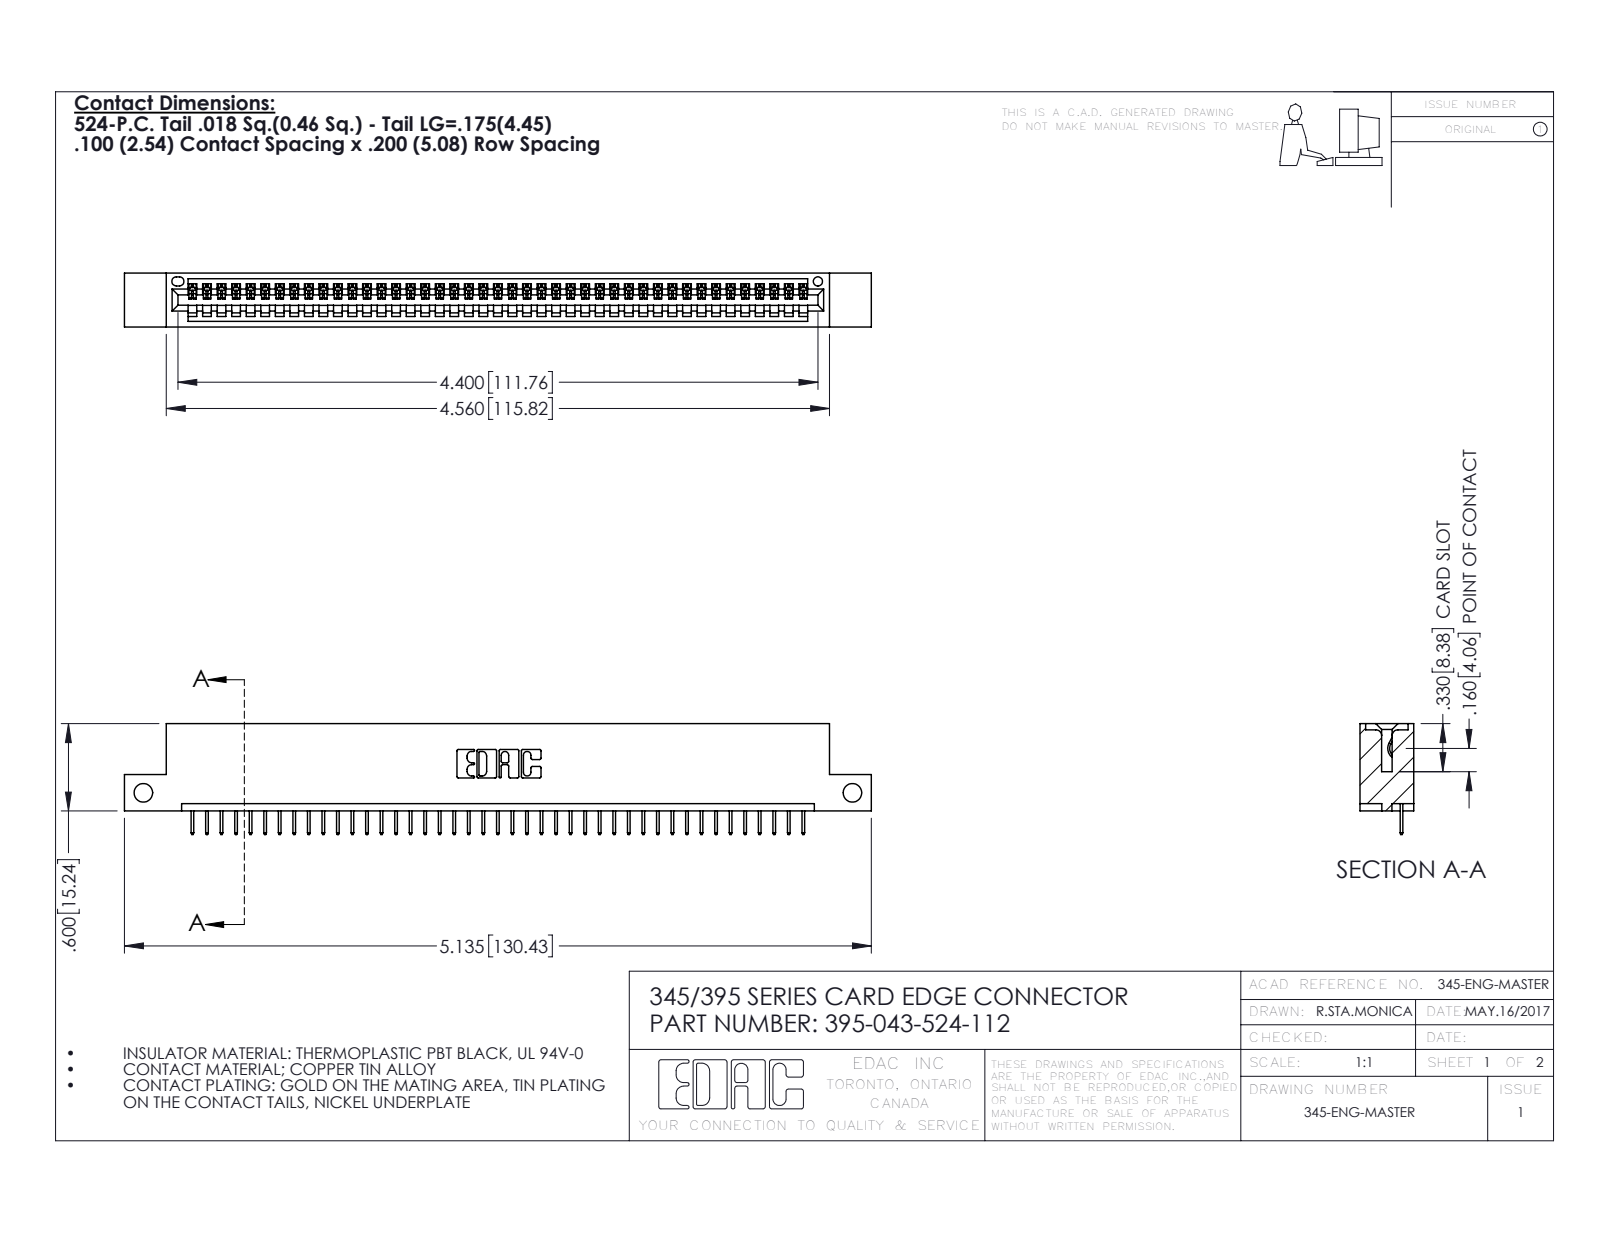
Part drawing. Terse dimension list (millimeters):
name: 395-043-524-112; 345-292-001_345-293-124; 345 Part_Flush Mounting Lugs - Side Mount
written by: SolidWorks 2016 (CONFIG_CONTROL_DESIGN)
unit: mm
bodies: 44 solids, 2792 faces (2058 planar, 734 cylindrical, 0 other)
size: 130.4 × 19.4 × 9.4
volume: 12 100 mm³; area: 15 460 mm²
holes: 2× ⌀3.3, 1× ⌀1.6
rounds: 86× R0.2, 22× R0.3, 6× R0.2, 6× R0.8, 3× R0.7, 2× R0.8, 2× R1, 1× R0.4
face distances: 7.6, 1.8, 9.4, 5.1, 2.5, 6.9, 0.6, 5.7, 1.8, 3.8
hole spacings: 123.8
